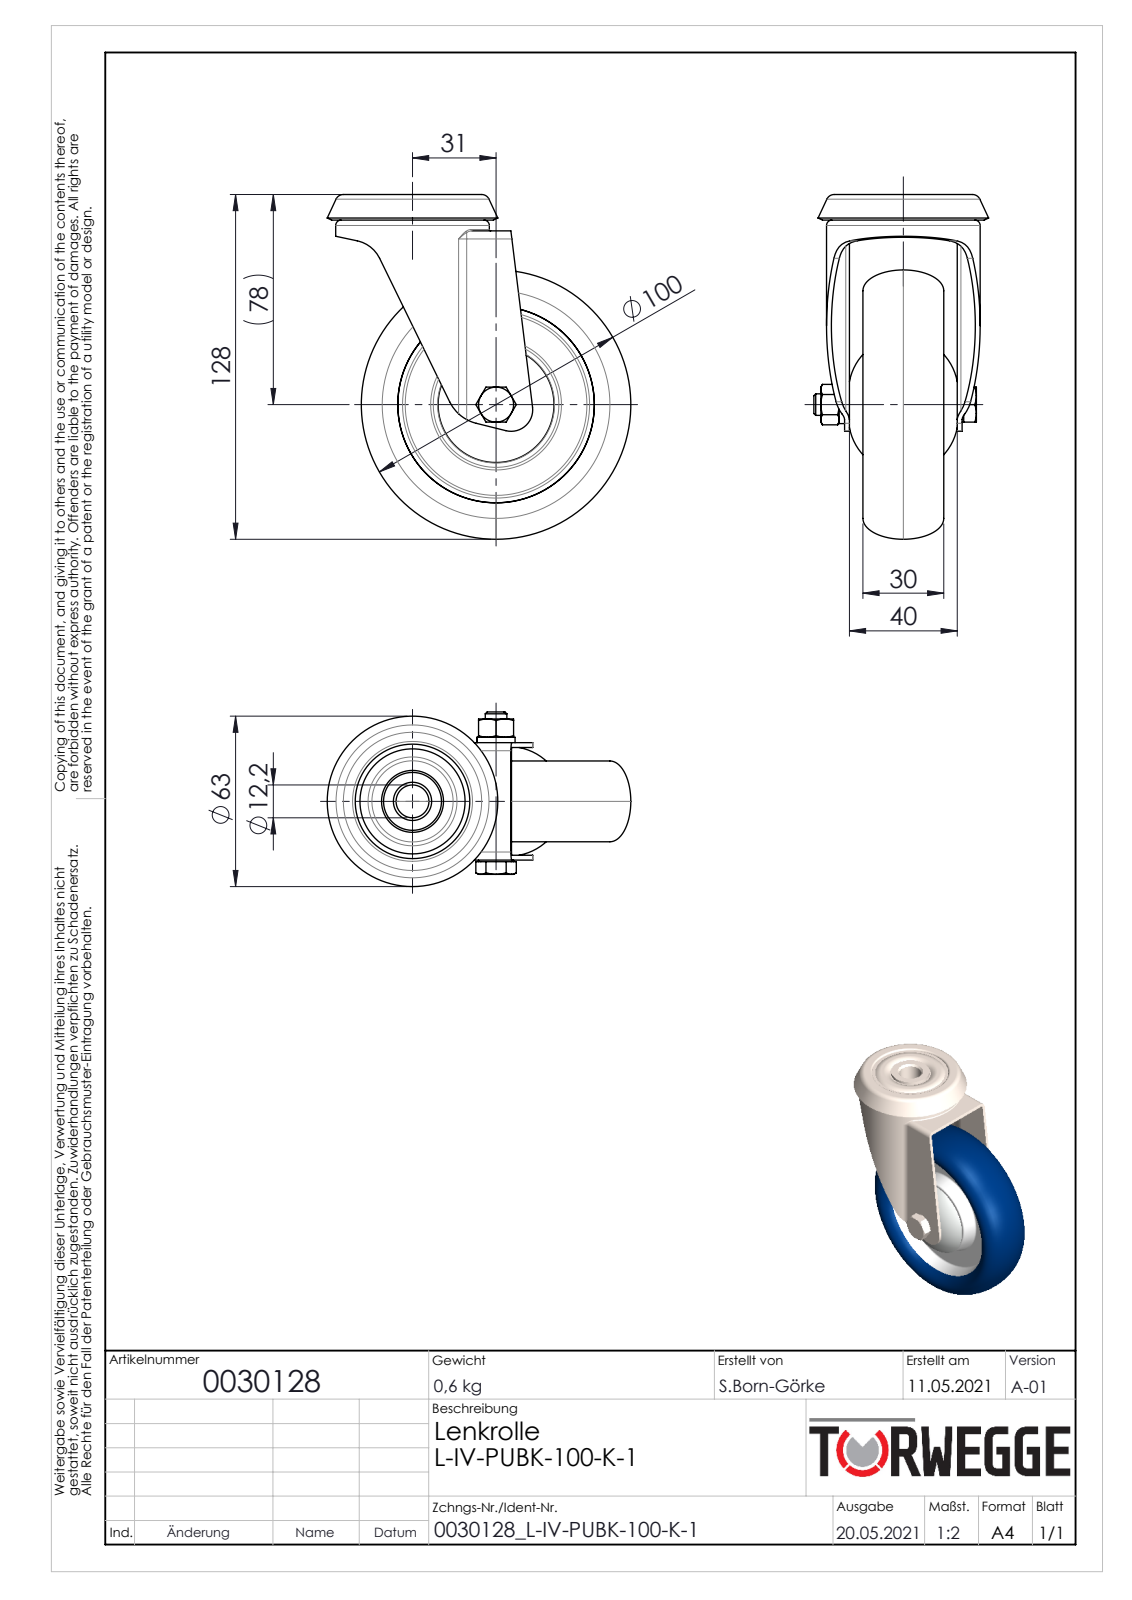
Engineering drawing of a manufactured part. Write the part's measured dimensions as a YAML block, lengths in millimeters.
part_name: "0030128"
step_written_by: "SolidWorks 2020 (AUTOMOTIVE_DESIGN)"
units: millimeters
bodies: {solids: 8, faces: 252, planar: 62, cylindrical: 54, other: 136}
overall_size: [128, 112.64, 64.84]
volume: 192725
surface_area: 83672
round_holes:
  - {diameter: 6.8, count: 1}
  - {diameter: 8, count: 1}
  - {diameter: 8.1, count: 1}
  - {diameter: 8.3, count: 1}
  - {diameter: 12.2, count: 1}
  - {diameter: 33, count: 1}
  - {diameter: 35, count: 1}
  - {diameter: 53.4, count: 1}
round_bosses_or_shafts:
  - {diameter: 57, count: 1}
  - {diameter: 29, count: 1}
  - {diameter: 21.5, count: 1}
  - {diameter: 15, count: 1}
  - {diameter: 14.1, count: 1}
  - {diameter: 13, count: 1}
partial_cylinders:
  - {radius: 1.2, count: 2}
  - {radius: 3, count: 2}
  - {radius: 5, count: 2}
  - {radius: 6.8, count: 2}
  - {radius: 8, count: 1}
  - {radius: 12.01, count: 1}
  - {radius: 15, count: 1}
face_to_face_distances: [1.8, 17, 23, 18.8, 24.8, 41.8, 11.3, 6, 13.5, 9.5]
